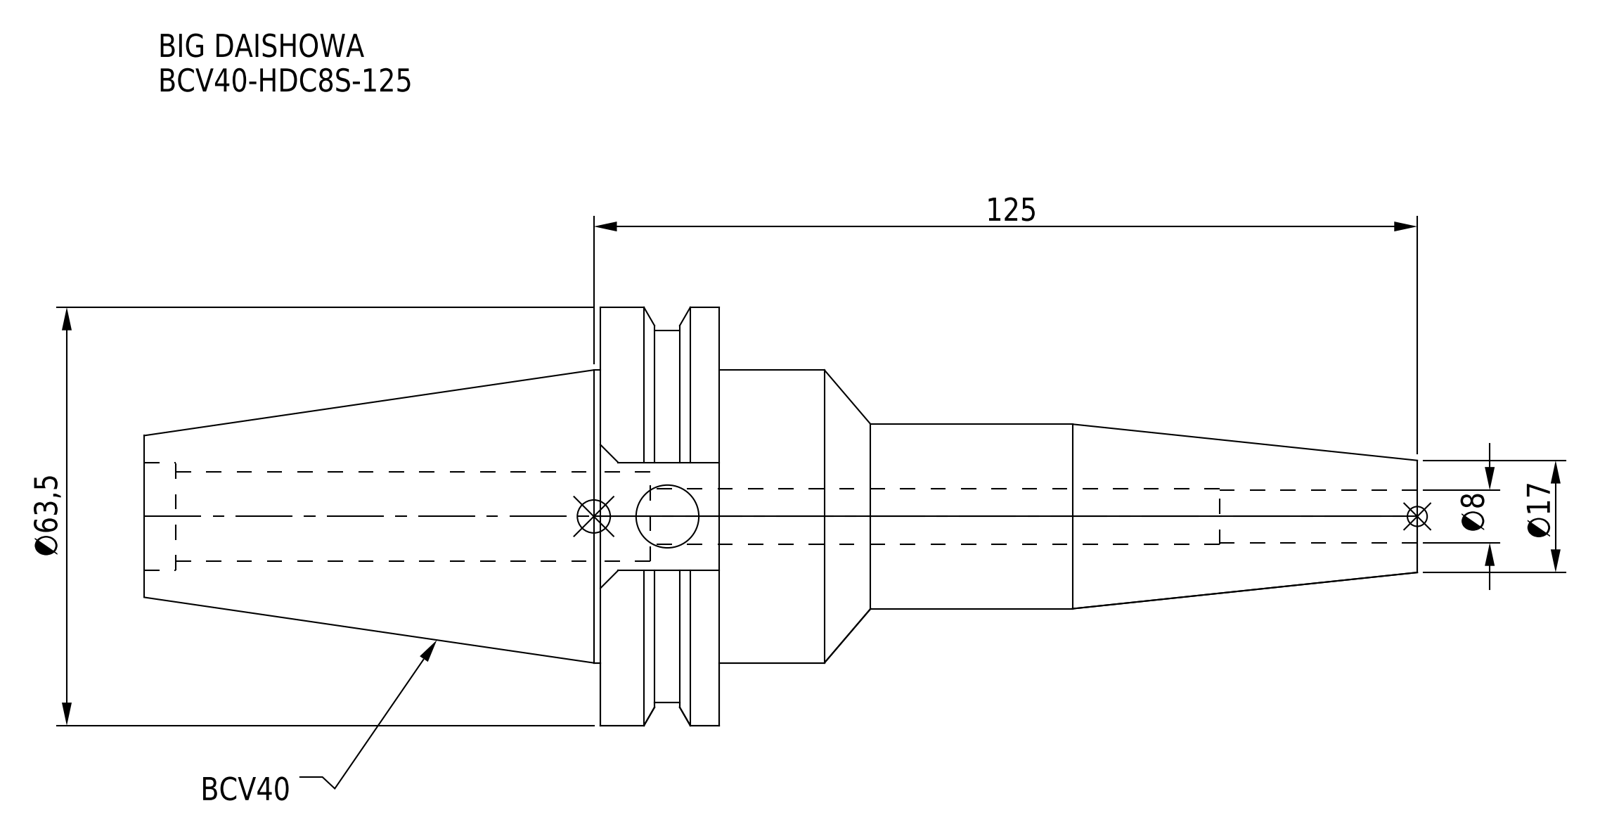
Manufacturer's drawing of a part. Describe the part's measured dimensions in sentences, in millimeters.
The part is named "BCV40-HDC8S-125". Its 3-D file was written by "CREO PARAMETRIC BY PTC INC, 2016380 (AUTOMOTIVE_DESIGN)". It is 1 solid with 56 faces: 22 planar, 24 cylindrical and 10 other. Overall it measures 193.25 by 63.5 by 61.35 millimeters. Its volume is 171 130 cubic millimeters and its surface area 31 807 square millimeters. Round holes: 1 of diameter 8, 1 of diameter 8.5, 1 of diameter 9.53, 1 of diameter 13.6, 1 of diameter 16.32. Round bosses or shafts: 1 of diameter 63.5, 1 of diameter 56.36, 1 of diameter 44.45, 1 of diameter 28. The main face-to-face distances are 18.05, 87.3, 69.25, 47.55, 105.95, 124, 193.25, 16.38, 111.95, 6.
